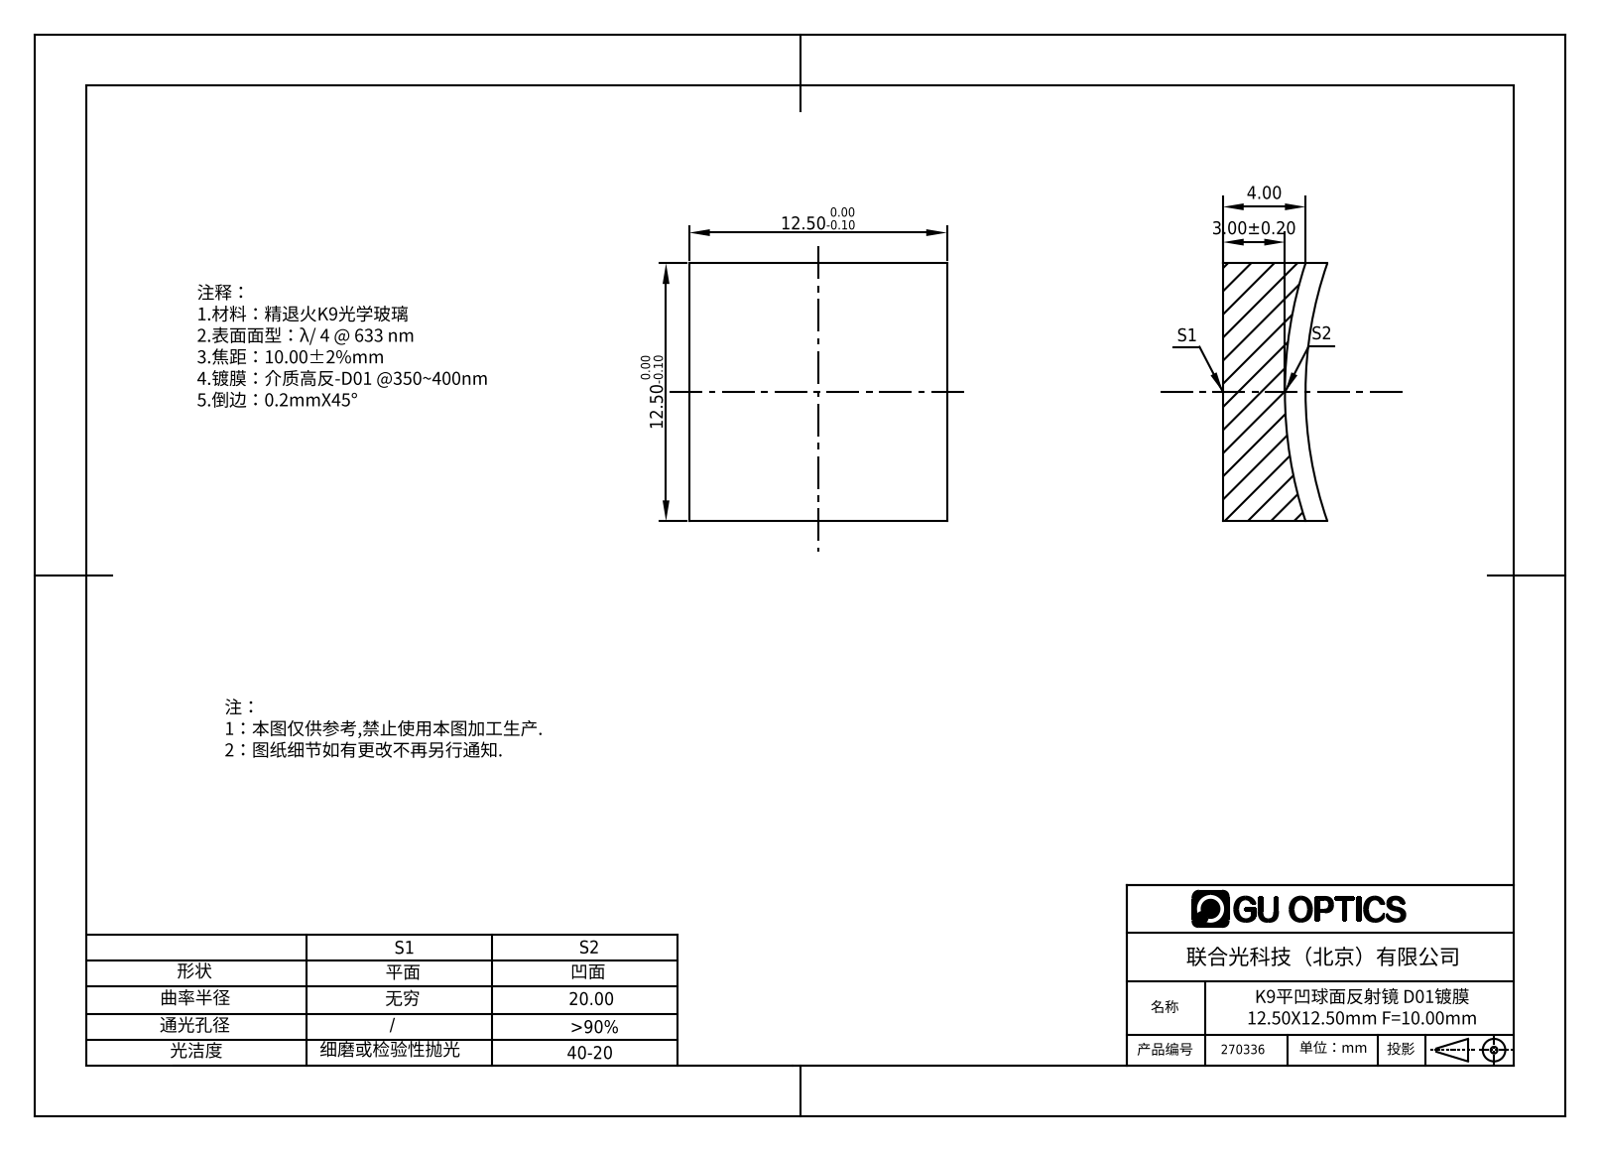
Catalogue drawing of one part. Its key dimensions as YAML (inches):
part_name: "270011"
step_written_by: "SolidWorks 2019 (AUTOMOTIVE_DESIGN)"
units: inches
bodies: {solids: 1, faces: 7, planar: 5, cylindrical: 0, other: 2}
overall_size: [0.492, 0.492, 0.199]
volume: 0.035
surface_area: 0.829
face_to_face_distances: [0.492]
